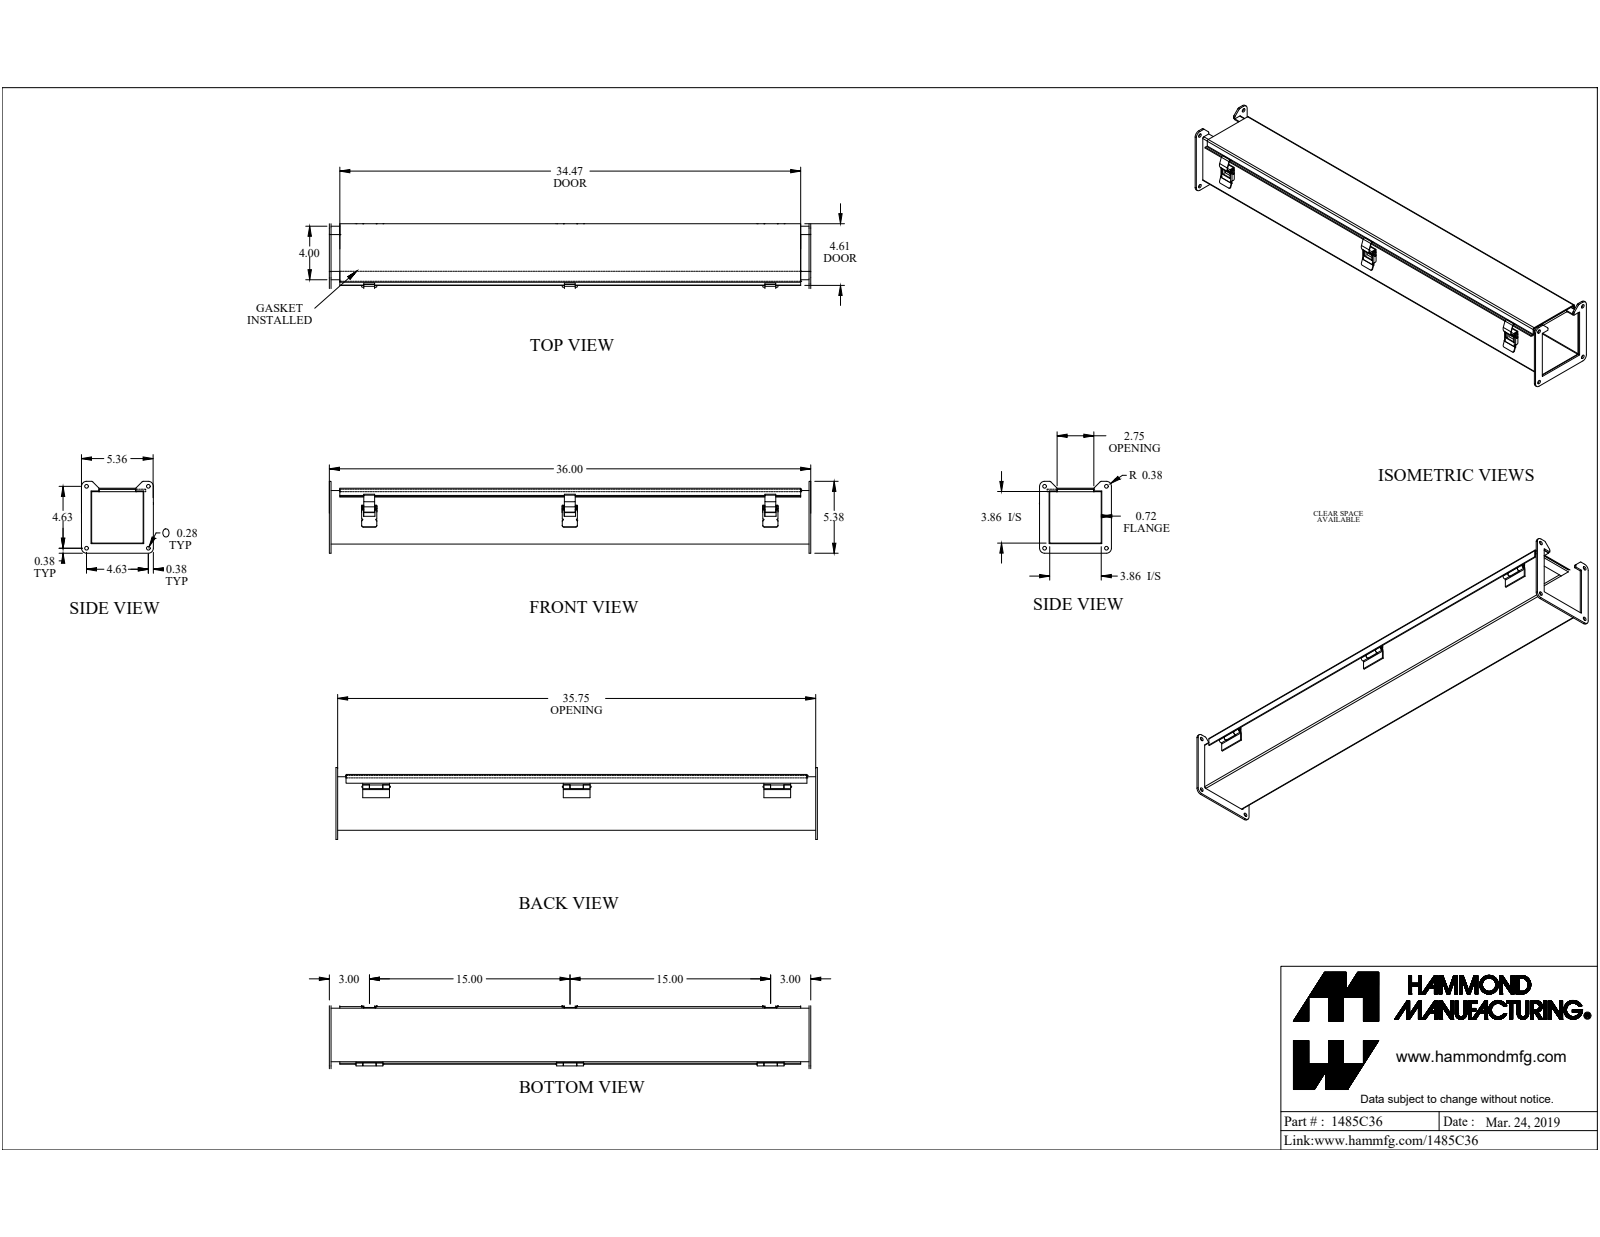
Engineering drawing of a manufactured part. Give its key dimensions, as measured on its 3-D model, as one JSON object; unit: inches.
{"part_name": "1485C36", "step_written_by": "SolidWorks 2019 (CONFIG_CONTROL_DESIGN)", "units": "inches", "bodies": {"solids": 26, "faces": 555, "planar": 334, "cylindrical": 215, "other": 6}, "overall_size": [36, 5.383, 5.375], "volume_in3": 62.01, "surface_area_in2": 1575, "round_holes": [[0.281, 4], [0.125, 1], [0.13, 1], [0.164, 1]], "round_bosses_or_shafts": [[0.187, 2], [0.275, 1], [0.156, 1], [0.125, 1]], "partial_cylinders_radius": [[0.016, 19], [0.125, 11], [0.035, 7], [0.036, 7], [0.039, 7], [0.076, 7], [0.108, 7], [0.015, 6]], "face_to_face_distances": [0.072, 3.928, 4.1, 4, 3.856, 4.172, 4.028, 0.172, 3.913, 3.841], "hole_center_spacings": [4.625, 6.541, 0.285, 1.075, 1.57, 1.849, 2.785, 3.057]}
